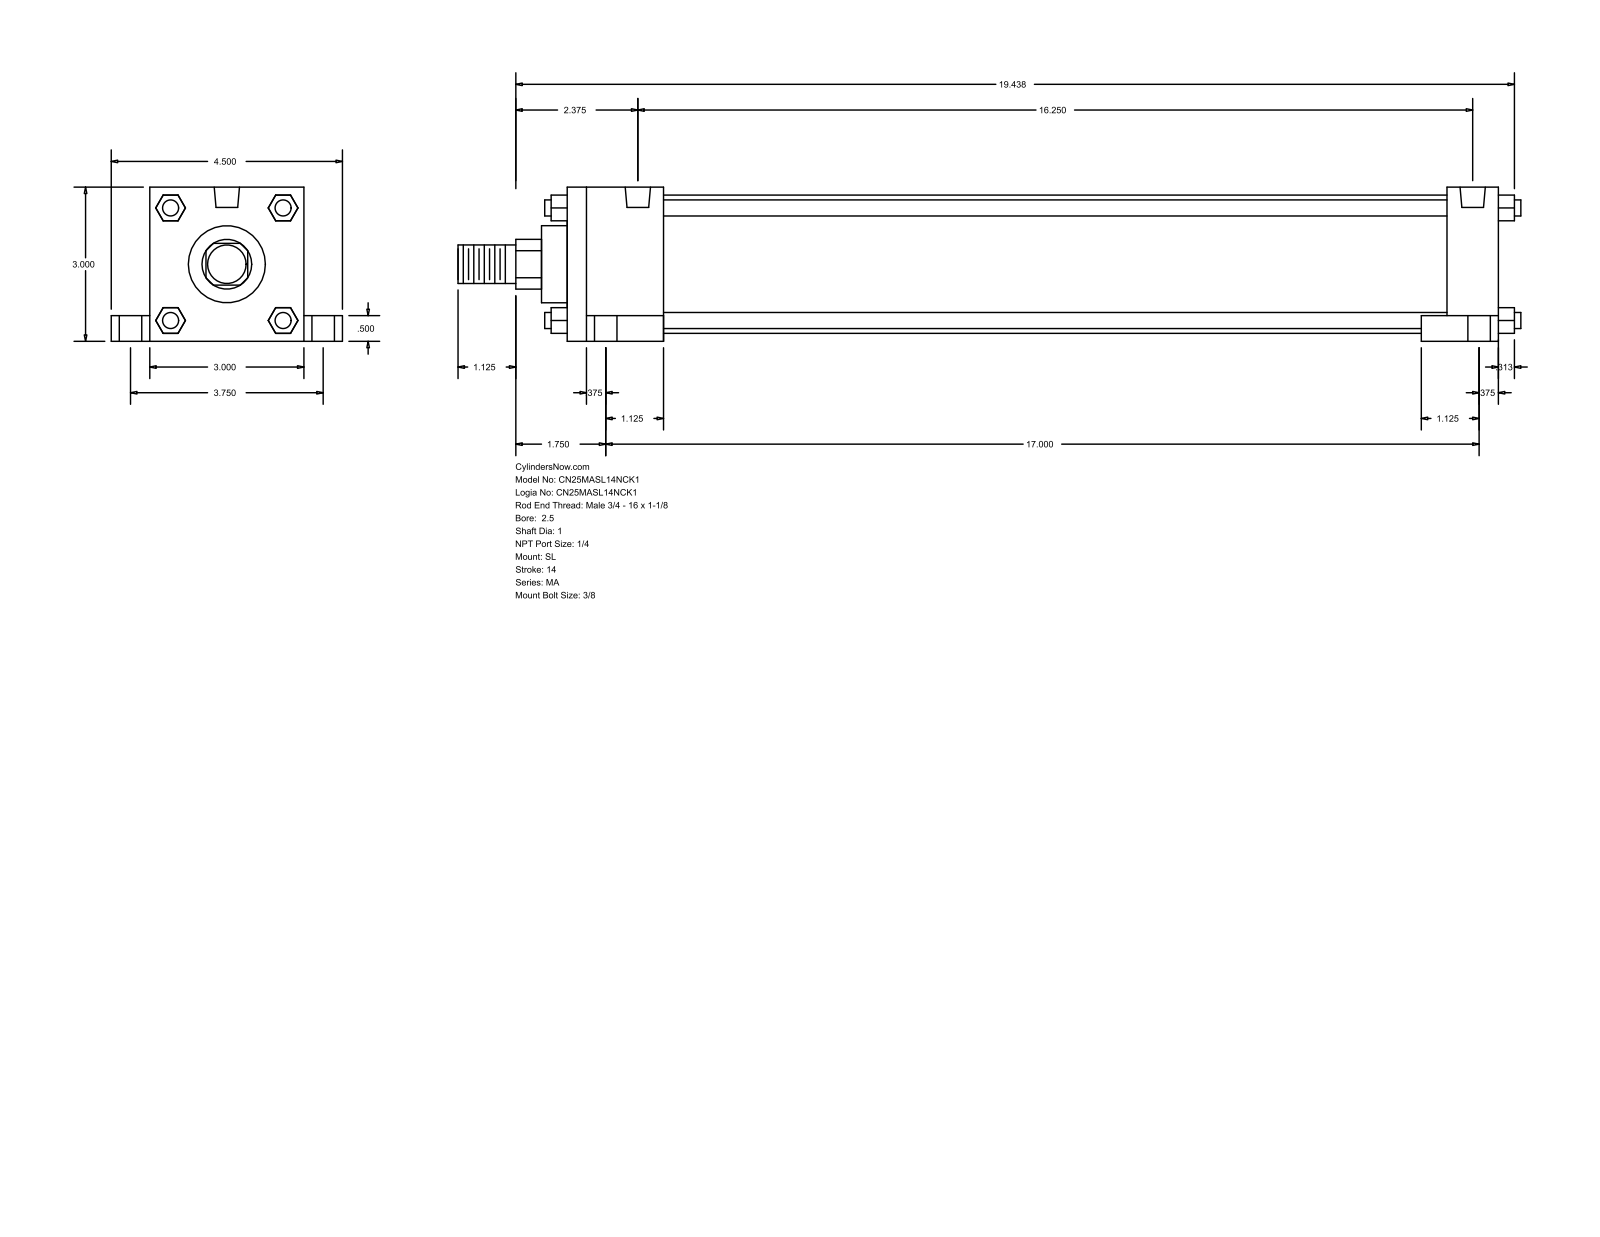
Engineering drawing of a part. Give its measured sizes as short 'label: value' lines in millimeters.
name: MA_SL__0250_1
written by: GSSL Pune (CONFIG_CONTROL_DESIGN)
unit: mm
bodies: 0 solids, 148 faces (112 planar, 36 cylindrical, 0 other)
size: 525.46 × 114.3 × 76.2
holes: 4× ⌀7.94, 4× ⌀11.11, 4× ⌀17.46, 2× ⌀12.49
bosses: 4× ⌀7.94, 1× ⌀68.33, 1× ⌀38.1, 1× ⌀25.4, 1× ⌀19.05
rounds: 1× R12.29
face distances: 76.2, 460.37, 12.7, 387.35, 25.39, 47.63, 412.74, 434.98, 19.05, 95.25
hole spacings: 47.73, 50.2, 95.24, 412.74, 418.64, 431.26, 431.8, 442.18
